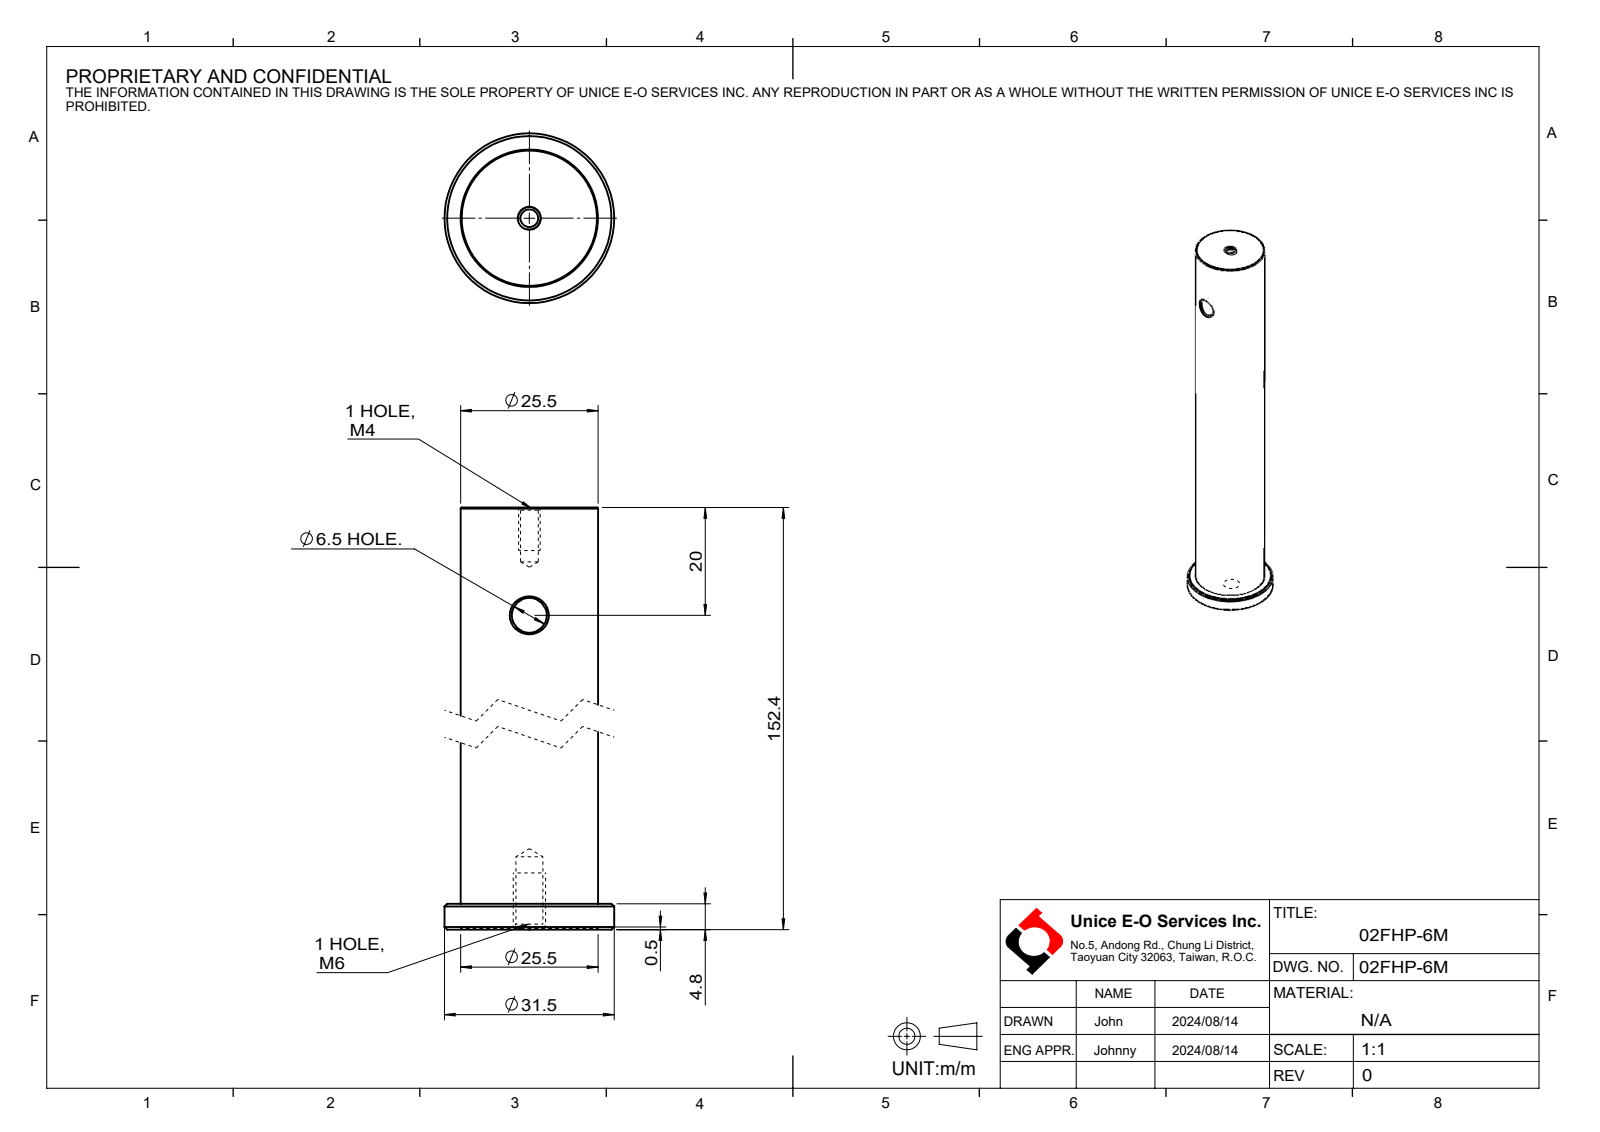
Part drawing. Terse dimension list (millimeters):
name: 02FHP-6M
written by: SolidWorks 2024 (CONFIG_CONTROL_DESIGN)
unit: mm
bodies: 1 solid, 38 faces (4 planar, 12 cylindrical, 22 other)
size: 152.4 × 31.5 × 31.5
volume: 77 641 mm³; area: 14 563 mm²
holes: 1× ⌀3.3, 1× ⌀5, 1× ⌀6.5, 1× ⌀25.5
bosses: 1× ⌀31.5
face distances: 151.9, 4.3, 147.6, 0.5, 4.8, 152.4
